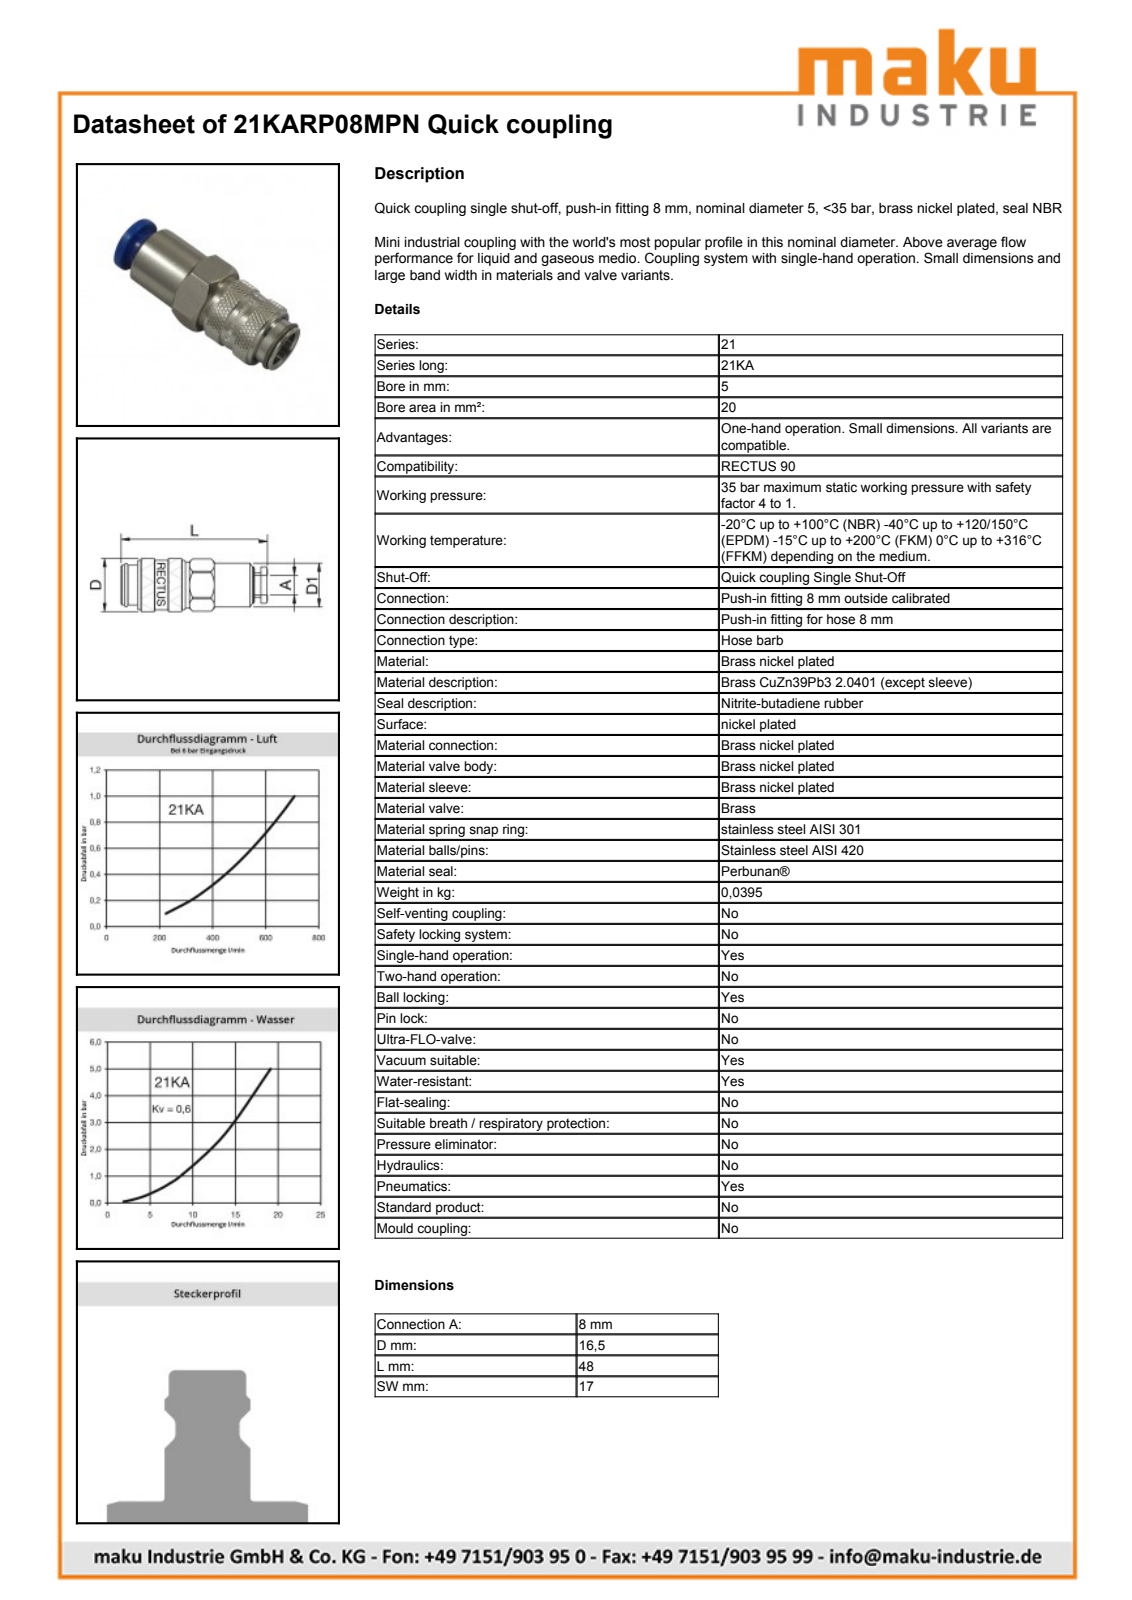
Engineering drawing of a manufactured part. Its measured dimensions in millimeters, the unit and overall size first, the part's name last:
Units: millimetres
Overall size (bounding box): 48.56 × 19.13 × 17.71
Round holes (diameter × count): ⌀12.15 ×1, ⌀14 ×1
Round bosses / shafts (diameter × count): ⌀16.15 ×1, ⌀15.3 ×1, ⌀15.1 ×1, ⌀13.05 ×1, ⌀12.65 ×1, ⌀12 ×1, ⌀11.15 ×1, ⌀9.3 ×1
Partial cylindrical surfaces — rounded edges, fillets, slot ends (radius × count): R5.58 ×1, R7.45 ×1, R9.57 ×1
Main face-to-face distances: 17, 2.5, 48.56, 46.06, 20.6, 25.46, 27.96, 43.56, 22.96, 5
Volume: 8 440 mm³ · Surface area: 4 242 mm²
Bodies: 2 solids, 460 faces (152 planar, 63 cylindrical, 245 other)
Part name (STEP PRODUCT): D105342
STEP written by: Autodesk Inventor 2011 (AUTOMOTIVE_DESIGN)
